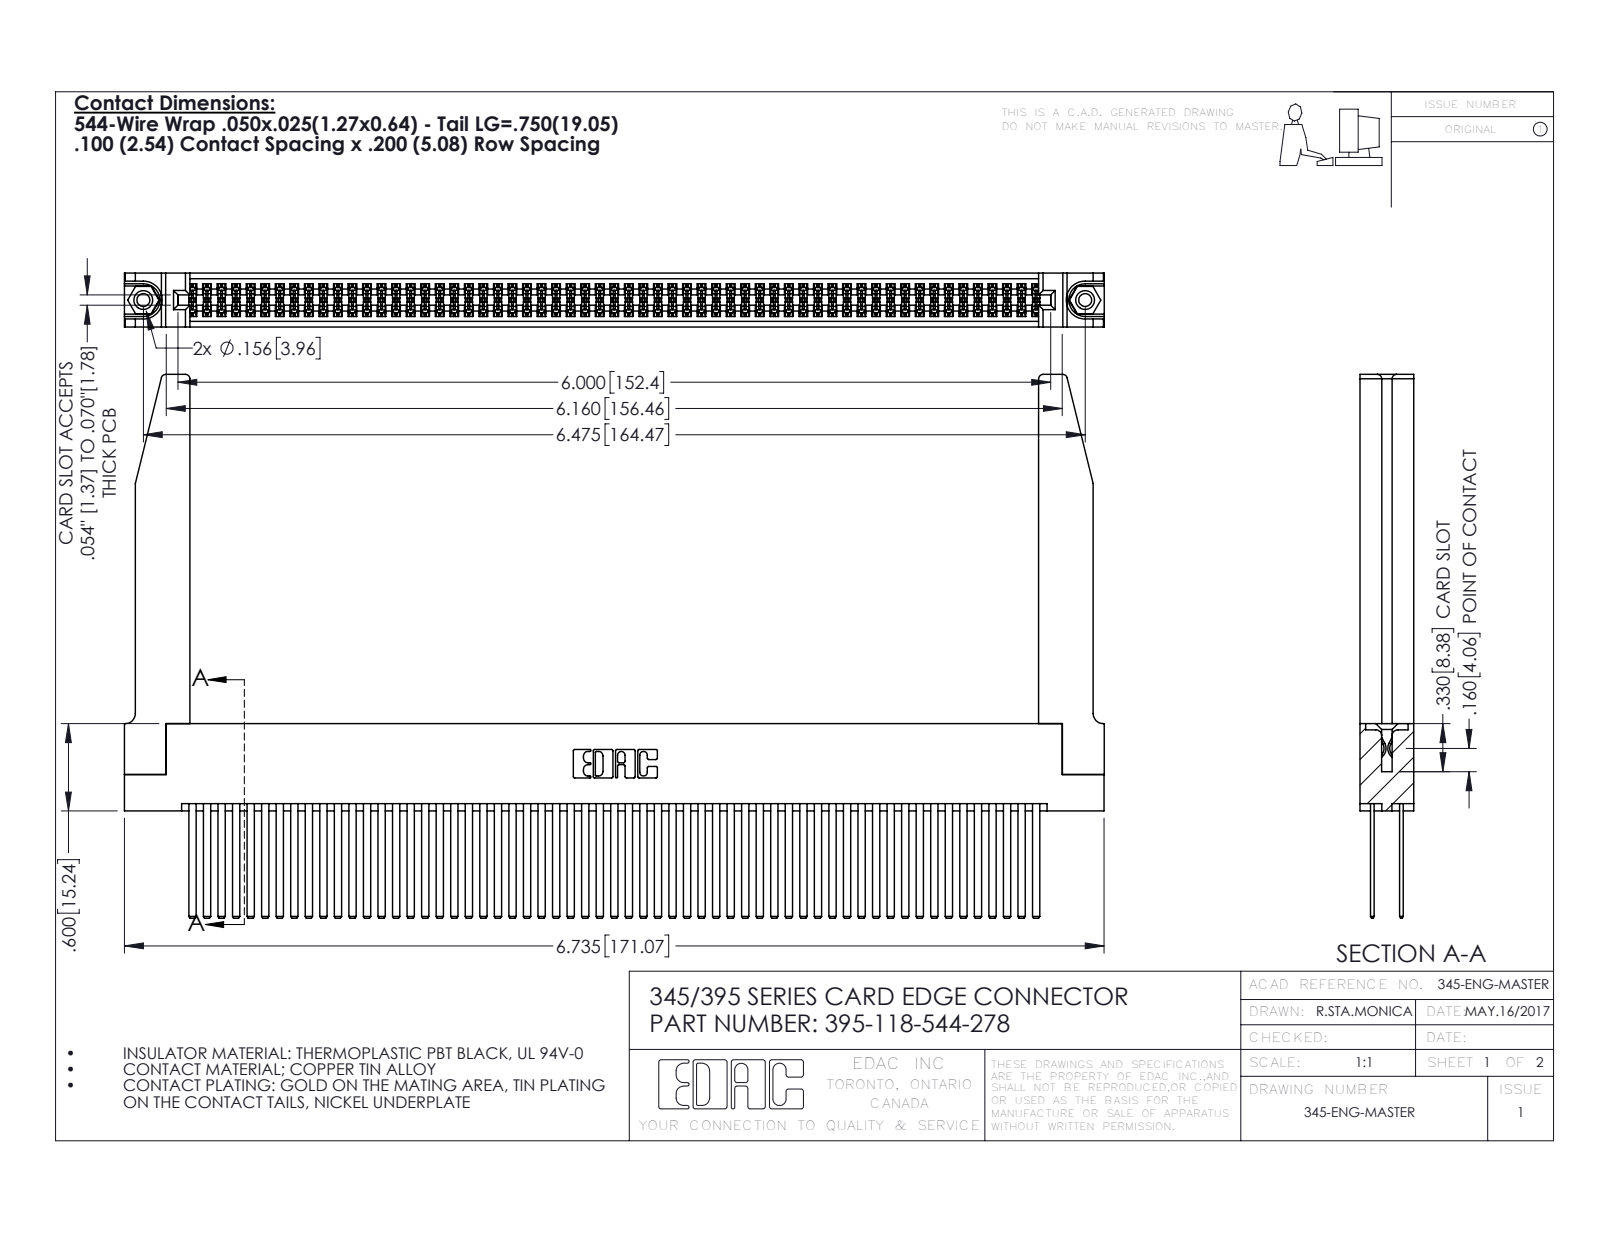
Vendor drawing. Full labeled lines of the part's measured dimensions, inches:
Part name (STEP PRODUCT): 345 Part_Flush Mounting Lugs - 0.156 Dia-TH; 345-250-001_345-250-001-102; 395-118-544-278; 345-220-078_345-220-078 (+1 more)
STEP written by: SolidWorks 2016 (CONFIG_CONTROL_DESIGN)
Units: inches
Bodies: 123 solids, 5552 faces (3644 planar, 1856 cylindrical, 52 other)
Overall size (bounding box): 6.736 × 3.737 × 0.37
Volume: 1.599 in³ · Surface area: 60.86 in²
Round holes (diameter × count): ⌀0.089 ×2, ⌀0.125 ×2, ⌀0.156 ×2, ⌀0.064 ×1
Round bosses / shafts (diameter × count): ⌀0.155 ×2
Partial cylindrical surfaces — rounded edges, fillets, slot ends (radius × count): R0.006 ×177, R0.01 ×22, R0.03 ×8, R0.007 ×6, R0.031 ×6, R0.026 ×3, R0.014 ×2, R0.019 ×2
Main face-to-face distances: 0.072, 0.298, 0.2, 0.098, 0.272, 0.025, 0.37, 0.225, 0.175, 0.148
Hole centre spacings: 0.27, 6.239, 6.475
